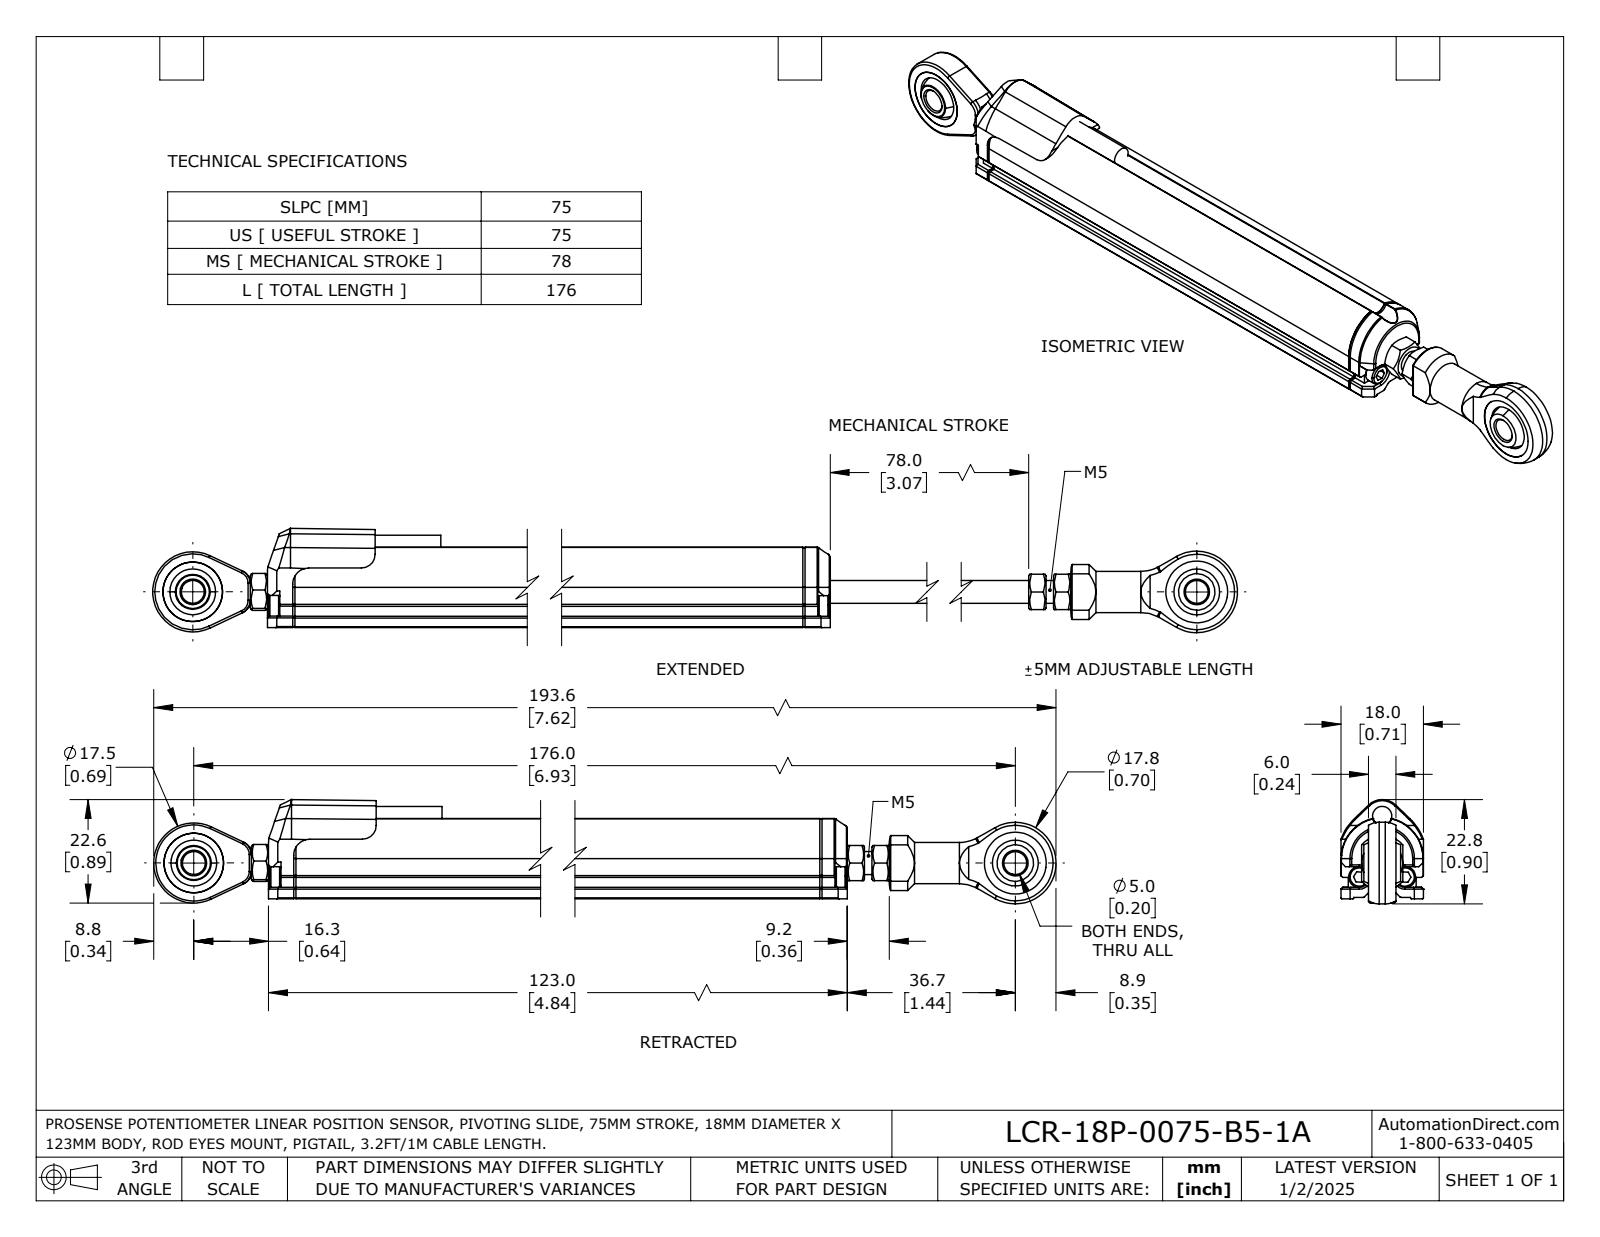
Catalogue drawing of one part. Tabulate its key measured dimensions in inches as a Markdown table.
| quantity | value |
| --- | --- |
| part name | LCR-18P-0075-B5-1A |
| STEP written by | SolidWorks 2023 (AUTOMOTIVE_DESIGN) |
| units | inches |
| bodies | 20 solids, 515 faces (289 planar, 136 cylindrical, 90 other) |
| overall size | 7.624 × 0.896 × 0.709 |
| volume | 2.368 in³ |
| surface area | 31.37 in² |
| round holes (diameter × count) | 0.197 × 4, 0.102 × 2, 0.104 × 2, 0.394 × 2, 0.213 × 1, 0.272 × 1, 0.512 × 1, 0.531 × 1 |
| round bosses / shafts (diameter × count) | 0.181 × 4, 0.113 × 3, 0.059 × 2, 0.354 × 1, 0.165 × 1, 0.113 × 1 |
| partial cylindrical surfaces (radius × count) | 0.008 × 12, 0.004 × 10, 0.02 × 8, 0.012 × 6, 0.018 × 6, 0.016 × 4, 0.039 × 4, 0.043 × 4 |
| main face-to-face distances | 0.02, 4.39, 0.236, 0.709, 0.059, 0.071, 4.37, 0.063, 0.646, 0.173 |
| hole center spacings | 0.231, 0.394, 0.23, 0.231, 6.929 |
